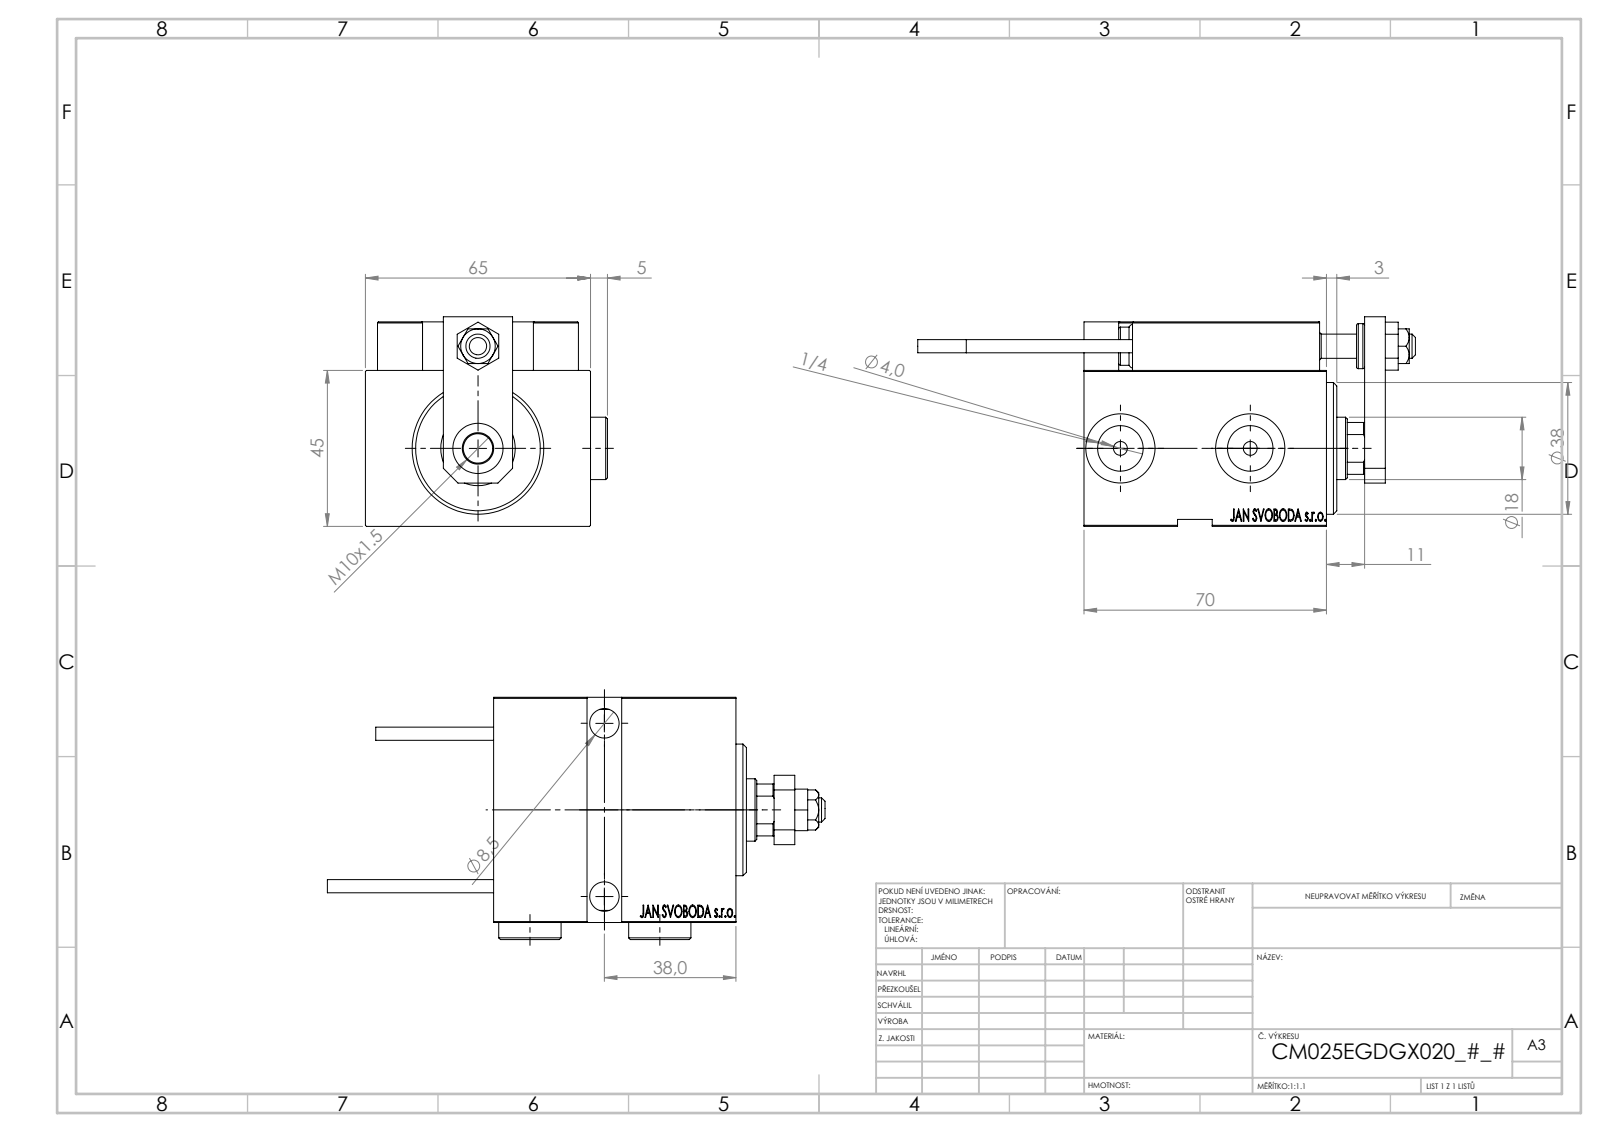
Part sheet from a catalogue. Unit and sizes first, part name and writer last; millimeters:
Units: millimetres
Overall size (bounding box): 143.7 × 69.9 × 60.5
Round holes (diameter × count): ⌀4 ×6, ⌀8 ×5, ⌀3.2 ×4, ⌀8.5 ×3, ⌀5 ×2, ⌀13.16 ×2, ⌀13.5 ×2, ⌀20 ×2, ⌀7 ×1, ⌀14.5 ×1, ⌀18 ×1, ⌀21.5 ×1
Round bosses / shafts (diameter × count): ⌀18 ×2, ⌀5 ×2, ⌀3.8 ×2, ⌀38 ×1, ⌀27 ×1, ⌀13 ×1, ⌀11 ×1
Partial cylindrical surfaces — rounded edges, fillets, slot ends (radius × count): R0.3 ×30, R3 ×2, R8.5 ×1
Main face-to-face distances: 45, 65, 59, 14, 6, 19, 8, 13, 70, 3
Hole centre spacings: 11.37, 20, 22.09, 29.59, 29.69, 30.89, 31.11, 34.17
Volume: 235 213 mm³ · Surface area: 66 338 mm²
Bodies: 26 solids, 1337 faces (602 planar, 190 cylindrical, 545 other)
Part name (STEP PRODUCT): ALLEN BOLT D8; ZARAZKA; Block; V450CM_E_VCP (+7 more)
STEP written by: SolidWorks 2019 (CONFIG_CONTROL_DESIGN)
